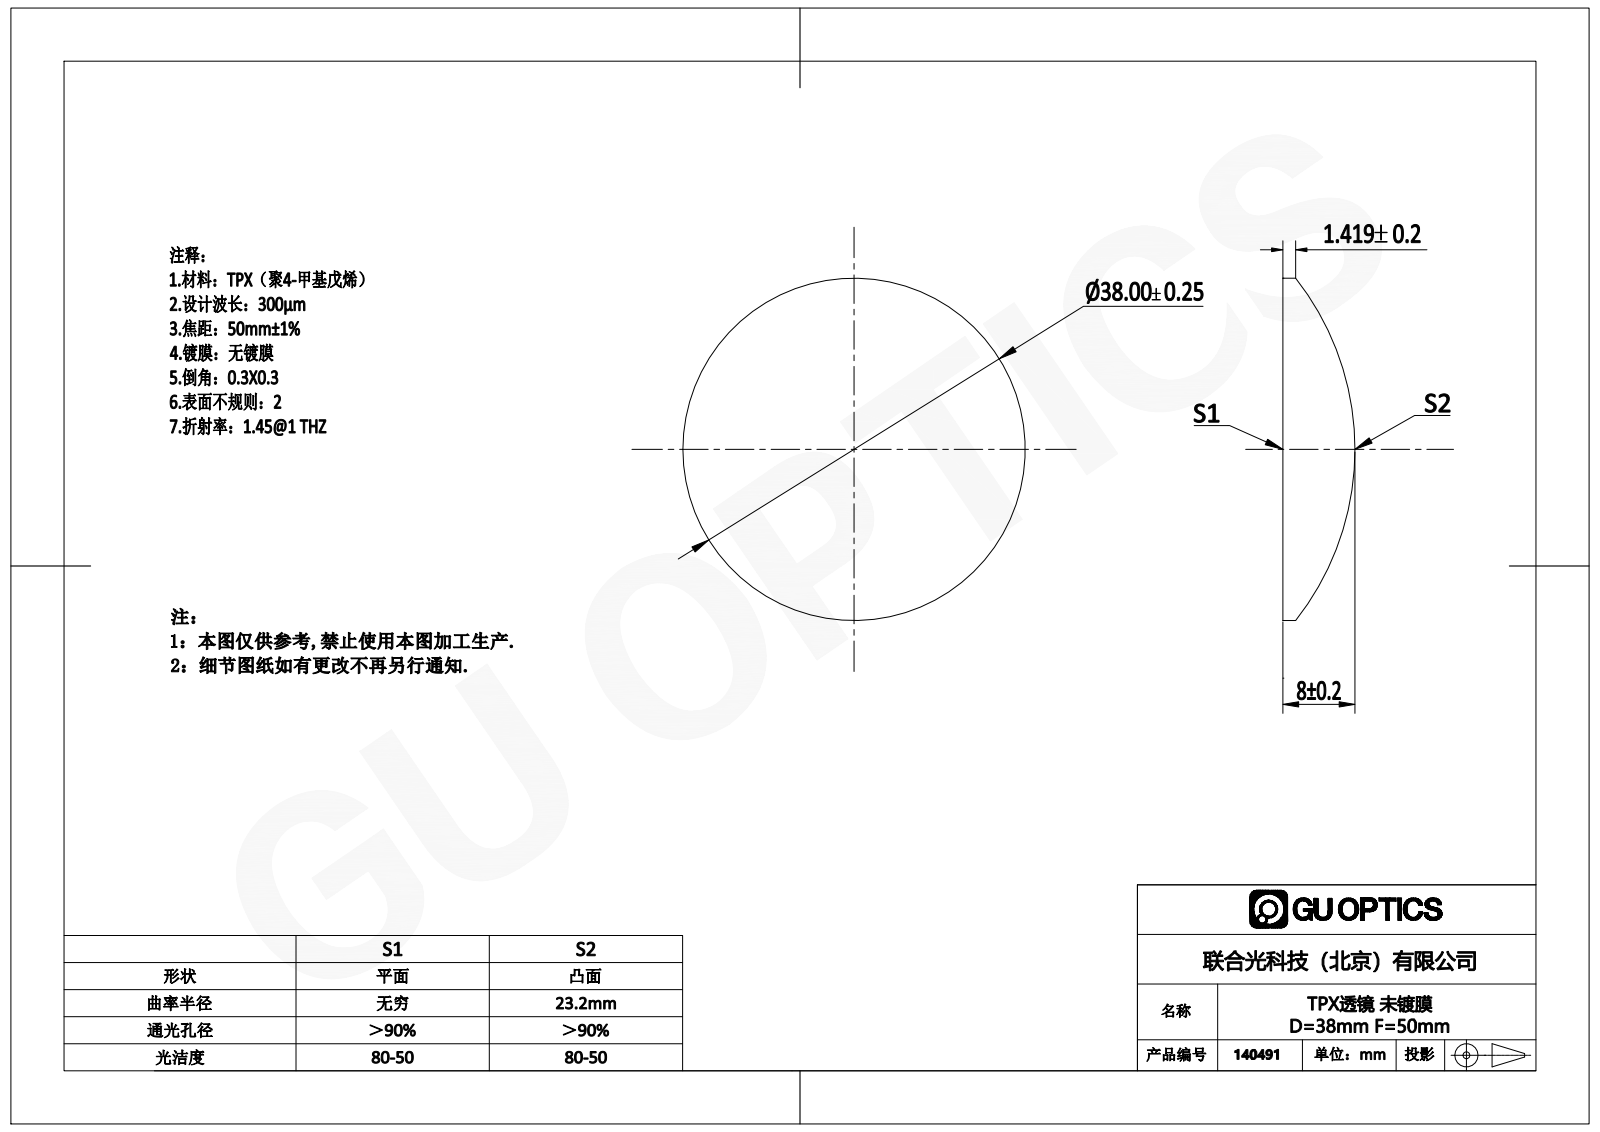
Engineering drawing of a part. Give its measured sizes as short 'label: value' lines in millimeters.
name: 140491
written by: SolidWorks 2020 (AUTOMOTIVE_DESIGN)
unit: mm
bodies: 1 solid, 5 faces (1 planar, 2 cylindrical, 2 other)
size: 38 × 38 × 8
volume: 5 490 mm³; area: 2 574 mm²
bosses: 1× ⌀38
